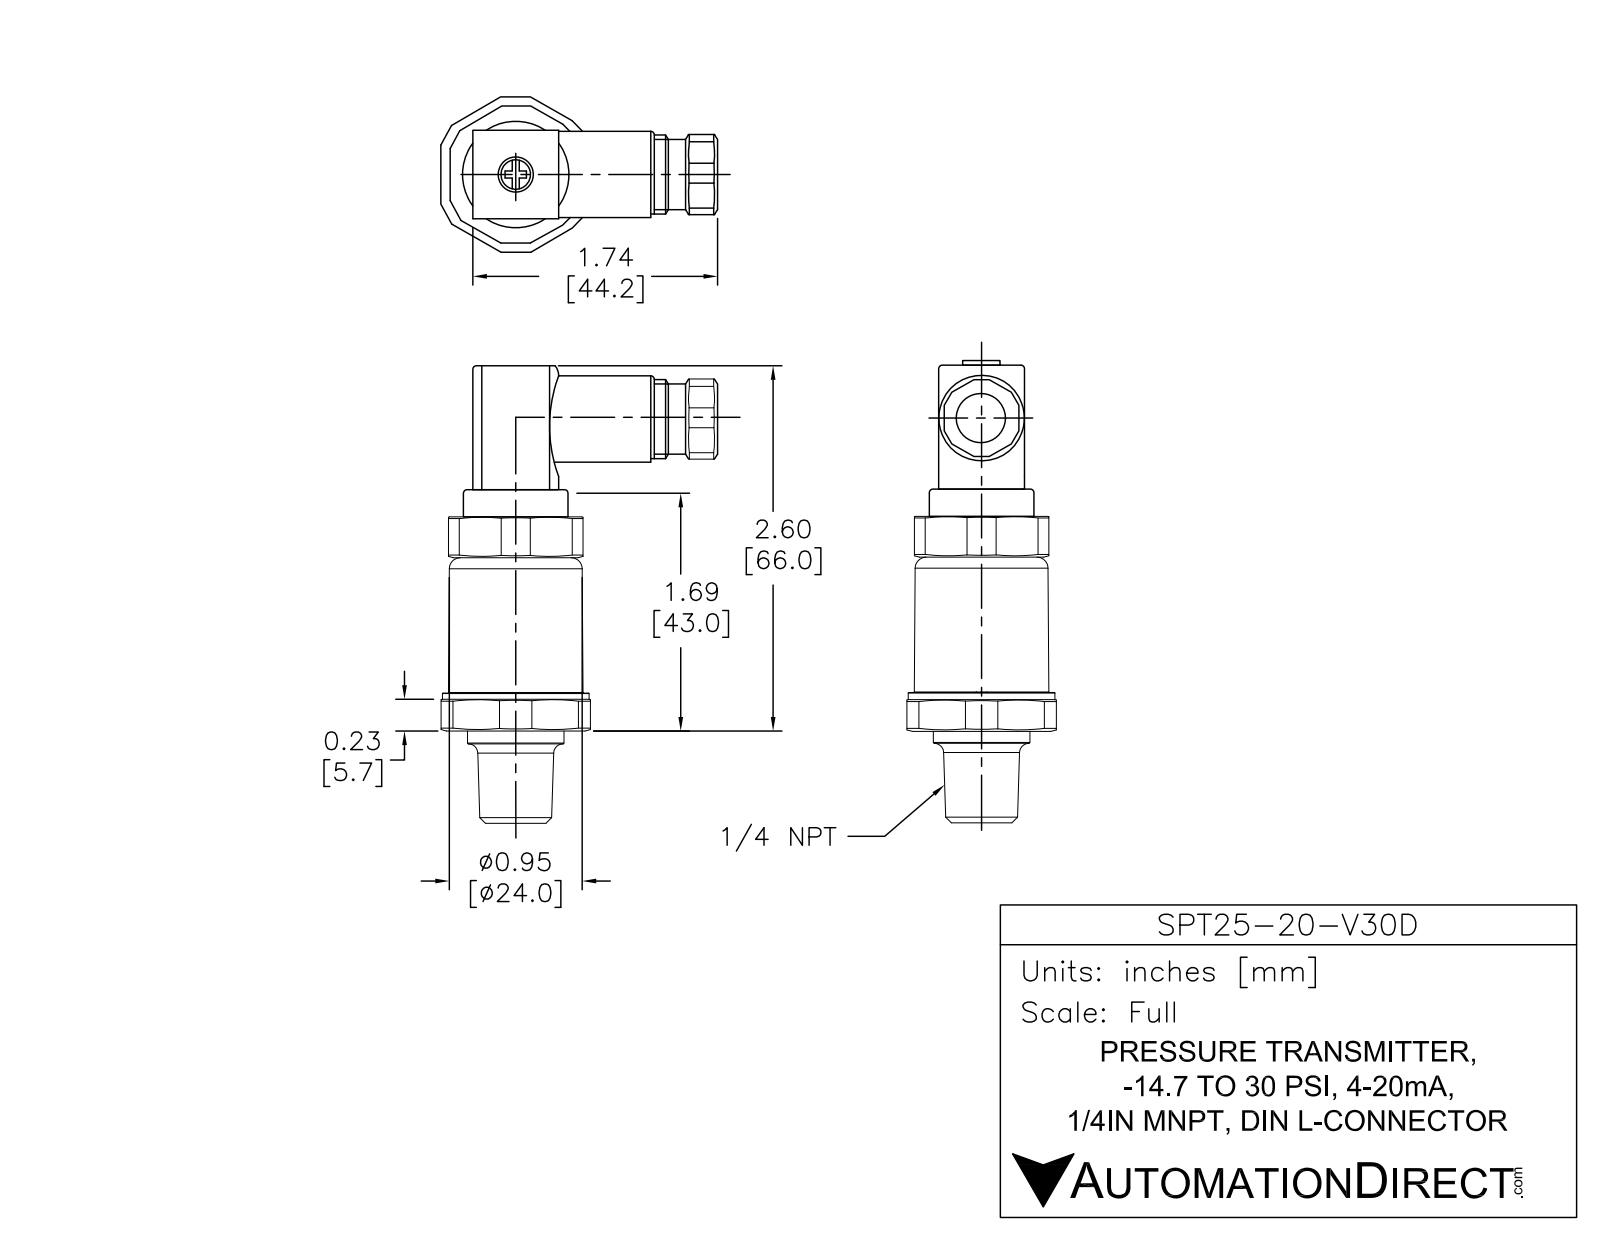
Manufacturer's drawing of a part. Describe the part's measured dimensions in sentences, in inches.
The part is named "SPT25-20-V30D". Its 3-D file was written by "SolidWorks 2011 (AUTOMOTIVE_DESIGN)". It is 7 solids with 75 faces: 32 planar, 27 cylindrical and 16 other. Overall it measures 6.035 by 1.142 by 1.067 inches. Its volume is 1.269 cubic inches and its surface area 11.11 square inches. Round holes: 1 of diameter 0.039, 1 of diameter 0.13. Round bosses or shafts: 6 of diameter 0.055, 5 of diameter 0.03, 1 of diameter 1.053, 1 of diameter 0.945, 1 of diameter 0.689, 1 of diameter 0.551, 1 of diameter 0.512, 1 of diameter 0.394. Partial cylindrical surfaces (rounded edges, fillets, slot ends): 1 of radius 0.079, 1 of radius 0.571. The main face-to-face distances are 0.266, 0.945, 0.679, 1.683, 1.949, 2.628, 1.732, 0.049, 0.217, 0.896.
